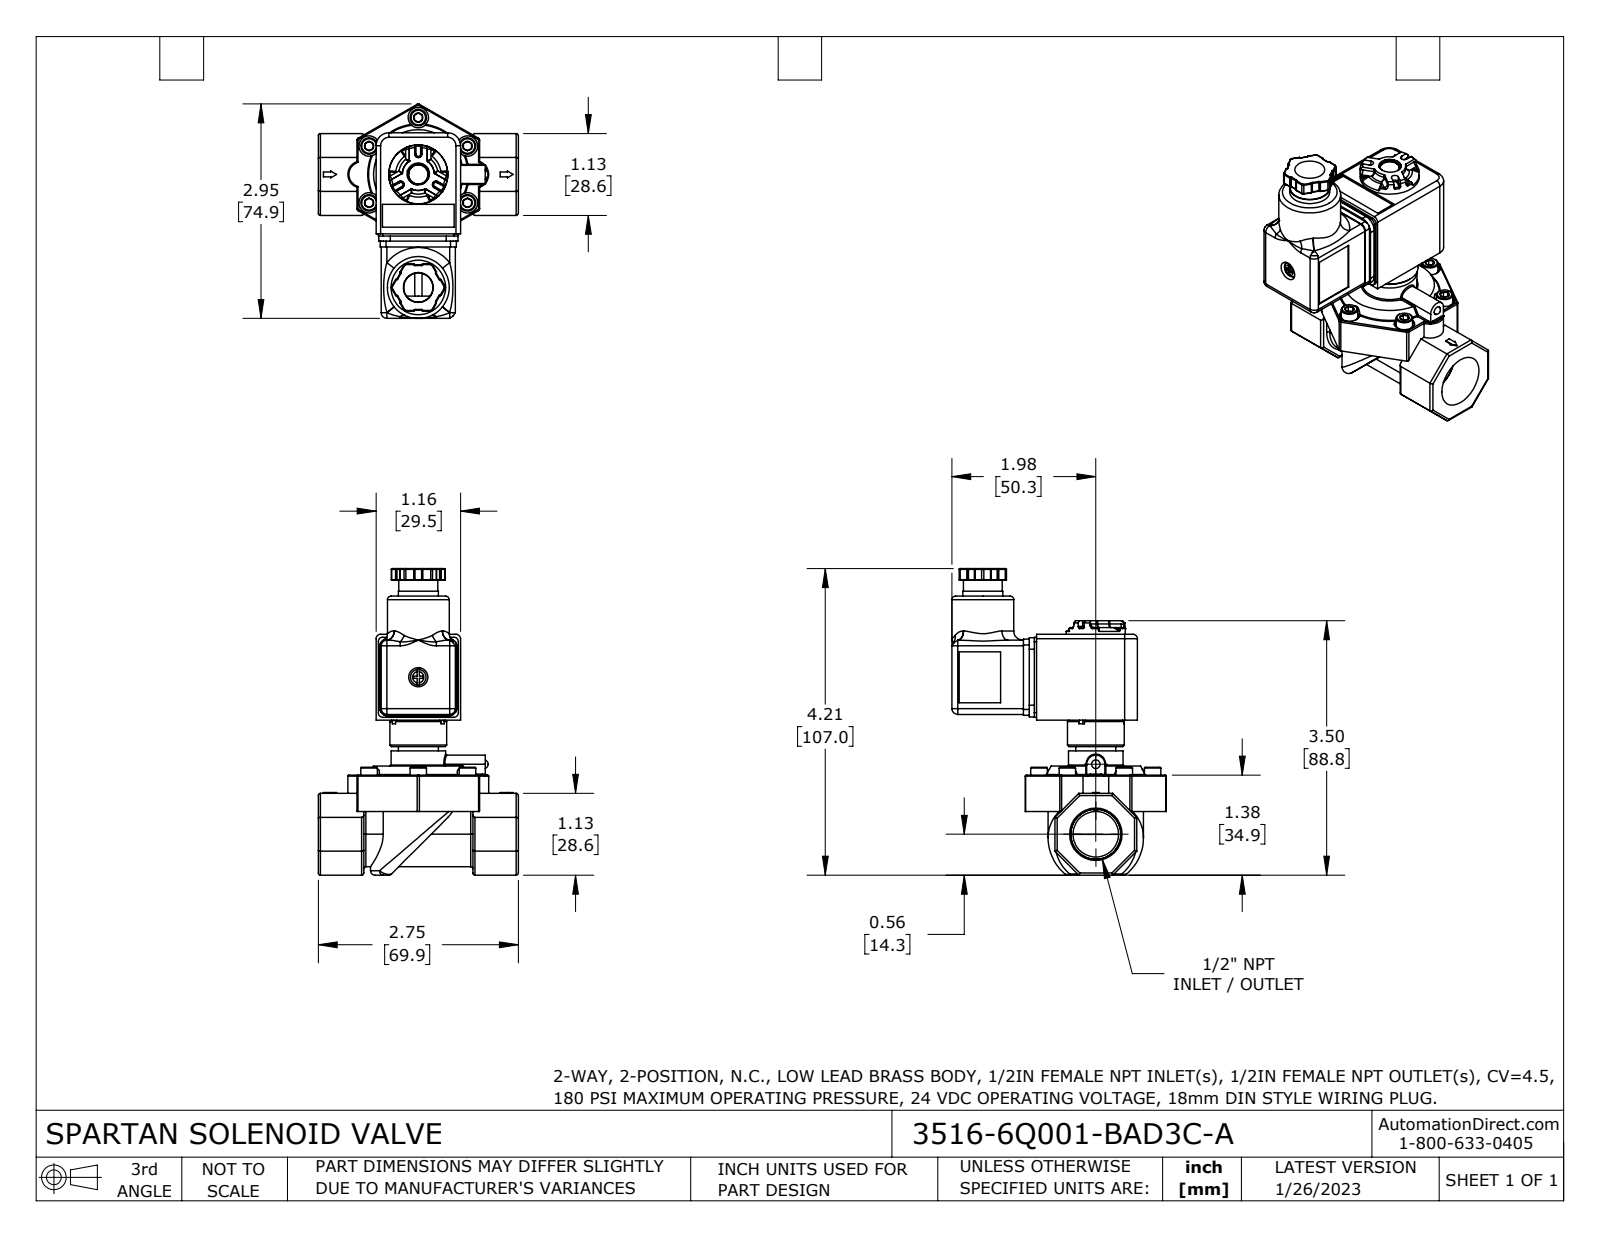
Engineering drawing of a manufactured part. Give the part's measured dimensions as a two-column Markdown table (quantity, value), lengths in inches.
| quantity | value |
| --- | --- |
| part name | 3516-6Q001-BAD3C-A |
| STEP written by | SolidWorks 2021 (CONFIG_CONTROL_DESIGN) |
| units | inches |
| bodies | 1 solid, 1634 faces (410 planar, 812 cylindrical, 412 other) |
| overall size | 4.213 × 2.948 × 2.75 |
| volume | 5.02 in³ |
| surface area | 64.57 in² |
| round holes (diameter × count) | 0.104 × 6, 0.156 × 6, 0.218 × 6, 0.281 × 6, 0.065 × 2, 0.093 × 2, 0.136 × 2, 0.625 × 2, 0.047 × 1, 0.062 × 1, 0.065 × 1, 0.09 × 1 |
| round bosses / shafts (diameter × count) | 0.212 × 7, 0.226 × 6, 0.138 × 6, 0.097 × 6, 0.156 × 2, 1.29 × 1, 0.85 × 1, 0.812 × 1 |
| partial cylindrical surfaces (radius × count) | 0.01 × 48, 0.02 × 39, 0.03 × 36, 0.015 × 23, 0.062 × 15, 0.08 × 12, 0.05 × 10, 0.125 × 9 |
| main face-to-face distances | 1.125, 0.118, 1.043, 0.048, 1.161, 0.25, 1.005, 1.687, 0.08, 0.794 |
| hole center spacings | 0.781, 1.353, 0.404, 1.105, 1.509, 1.562, 0.71, 0.8 |
